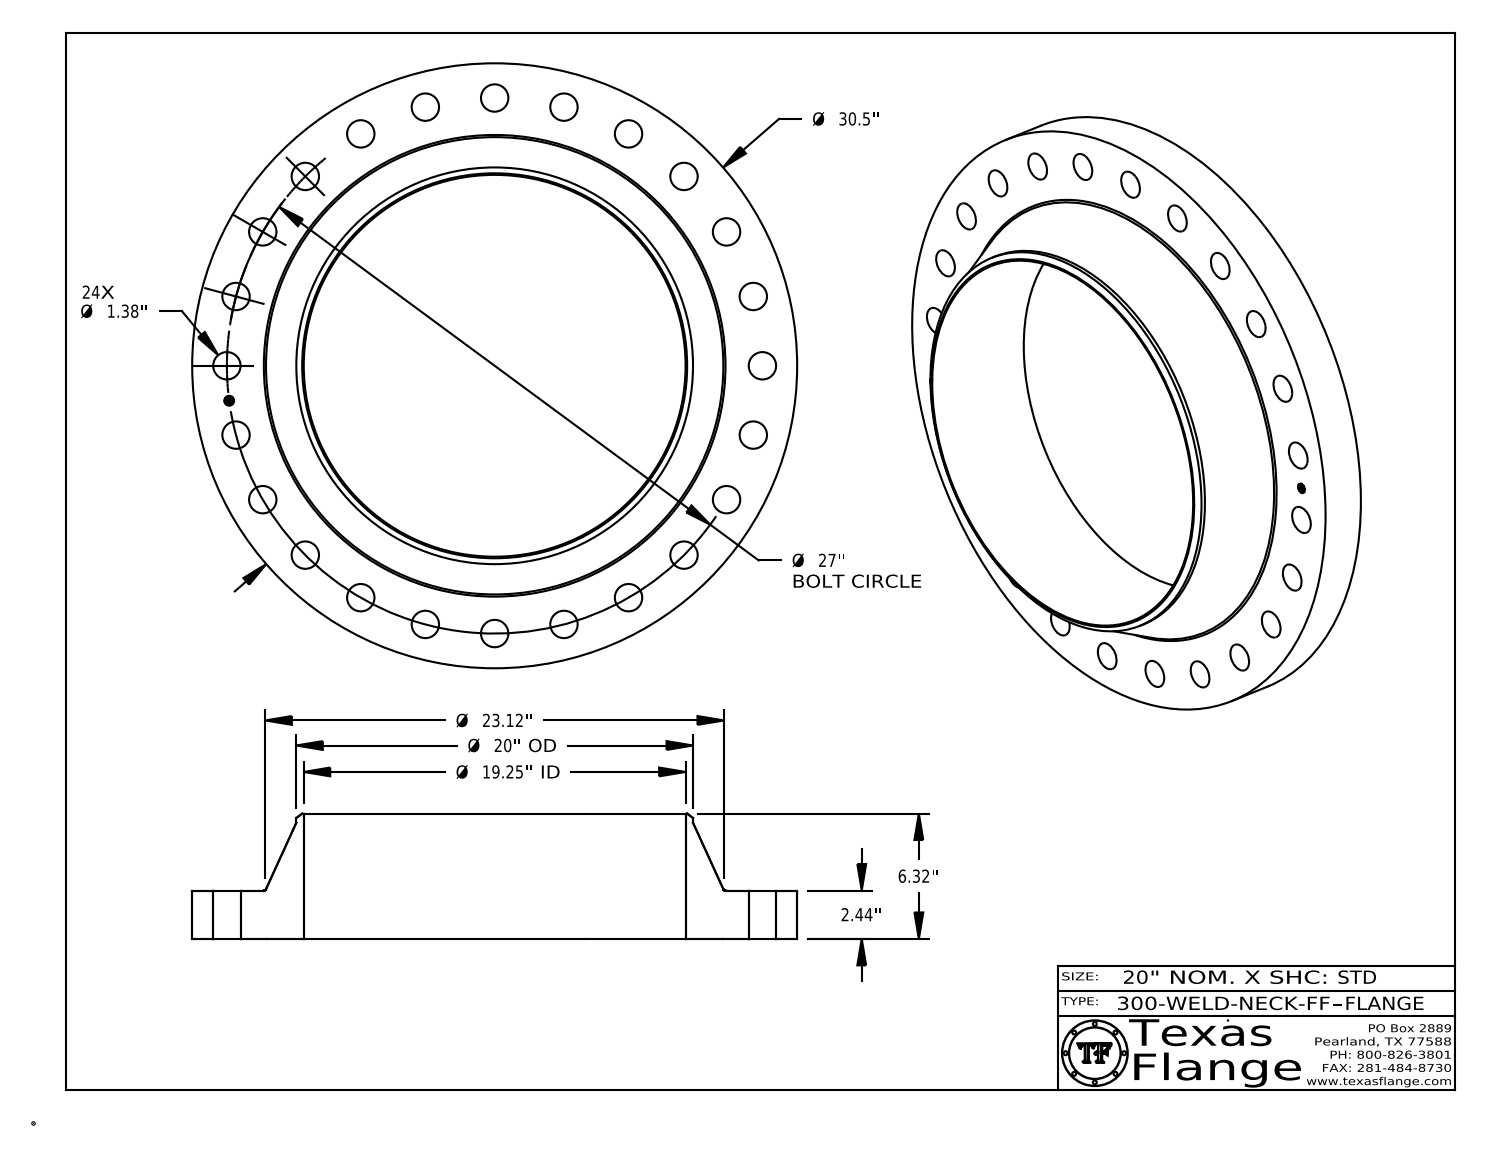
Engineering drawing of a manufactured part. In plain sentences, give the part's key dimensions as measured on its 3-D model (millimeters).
The part is named "300-WELD-NECK-FF". Its 3-D file was written by "CATIA V5 STEP AP214 (AUTOMOTIVE_DESIGN)". It is 1 solid with 449 faces: 369 planar, 74 cylindrical and 6 other. Overall it measures 774.7 by 774.7 by 160.5 millimeters. Its volume is 20 470 000 cubic millimeters and its surface area 1 190 000 square millimeters. Round holes: 24 of diameter 35.1, 1 of diameter 12.6, 1 of diameter 489. Round bosses or shafts: 8 of diameter 0.8, 1 of diameter 774.7, 1 of diameter 508, 1 of diameter 9.9. The main face-to-face distances are 62, 160.5, 98.6, 61.6, 0.4, 98.9, 3.8, 3.7, 0.7, 2.4. The hole center spacings are 342.9, 89.5, 177.5, 262.5, 417.5, 633.6, 679.9, 544.1.
